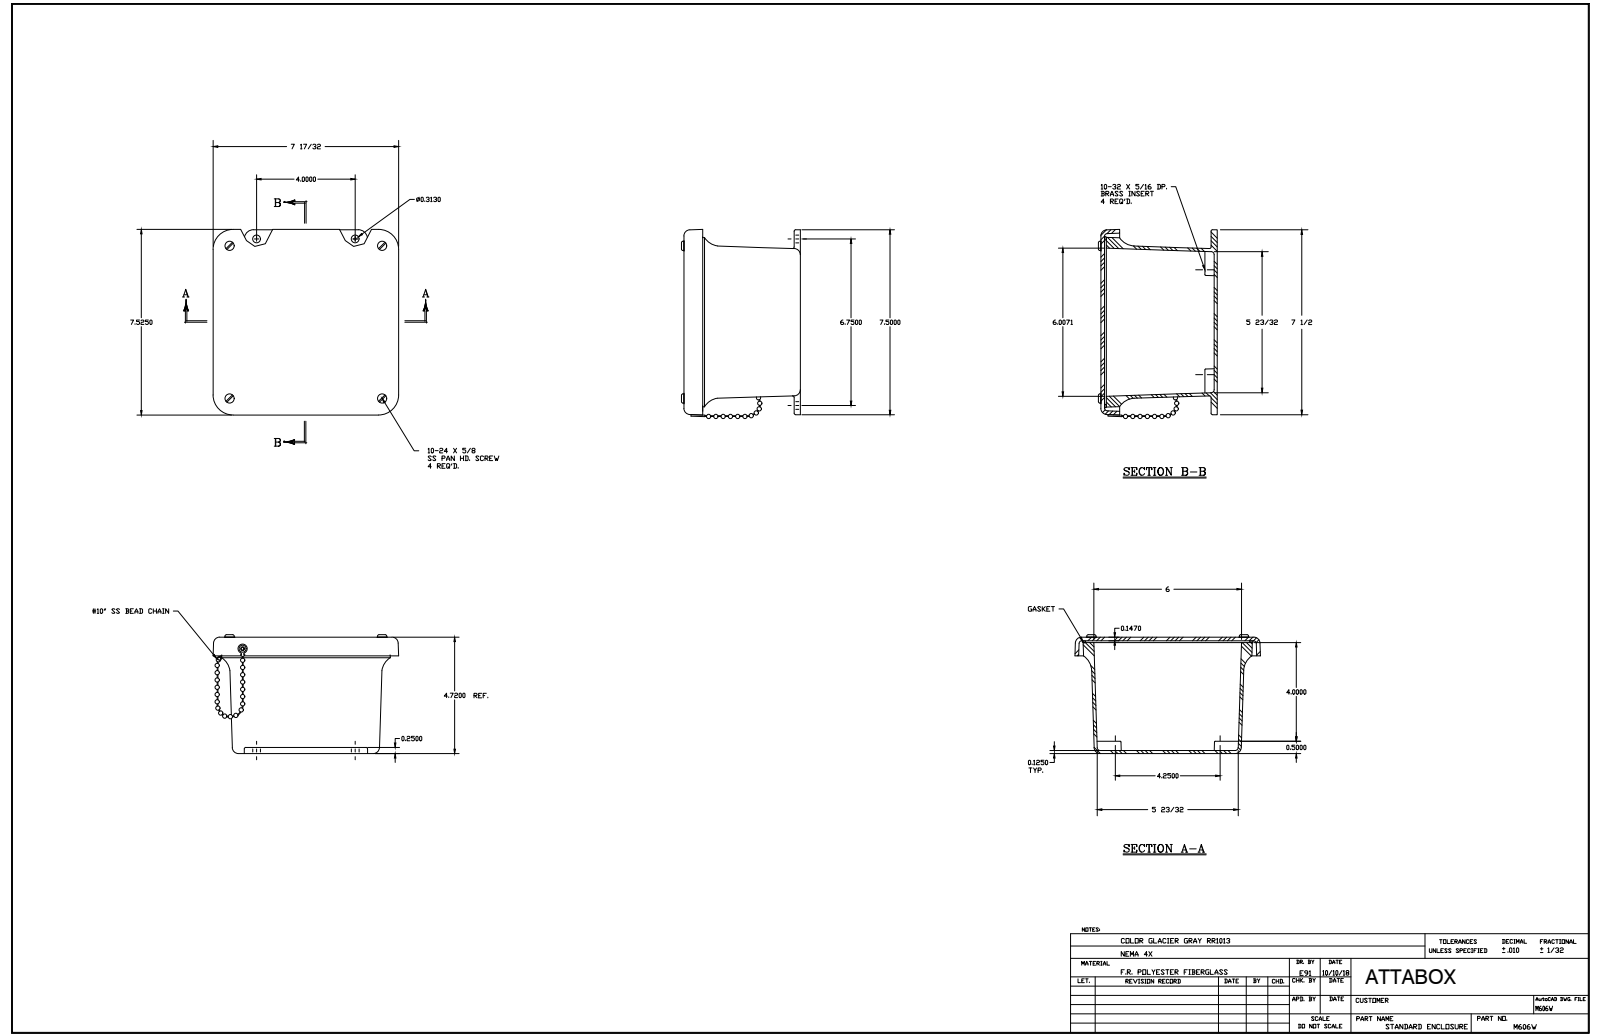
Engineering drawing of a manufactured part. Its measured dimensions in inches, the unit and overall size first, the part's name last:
Units: inches
Overall size (bounding box): 8.065 × 7.723 × 4.955
Round holes (diameter × count): ⌀0.152 ×5, ⌀0.145 ×4, ⌀0.156 ×4, ⌀0.218 ×4, ⌀0.14 ×3, ⌀0.187 ×2, ⌀0.126 ×1
Round bosses / shafts (diameter × count): ⌀0.27 ×8, ⌀0.19 ×4, ⌀0.156 ×4, ⌀0.25 ×2, ⌀0.375 ×1, ⌀0.375 ×1, ⌀0.283 ×1, ⌀0.125 ×1
Partial cylindrical surfaces — rounded edges, fillets, slot ends (radius × count): R0.031 ×20, R0.25 ×12, R0.125 ×8, R0.2 ×8, R0.063 ×4, R0.375 ×4, R0.75 ×4, R0.01 ×2
Main face-to-face distances: 0.147, 4.677, 4.824, 0.125, 4.552, 4.699, 0.152, 4.5, 4.625, 0.052
Hole centre spacings: 5.308, 1.37, 4.25, 6.187, 7.38, 6.01, 8.75, 4
Volume: 37.59 in³ · Surface area: 490.1 in²
Bodies: 45 solids, 888 faces (185 planar, 289 cylindrical, 414 other)
Part name (STEP PRODUCT): M606W
STEP written by: SolidWorks 2018 (AUTOMOTIVE_DESIGN)
